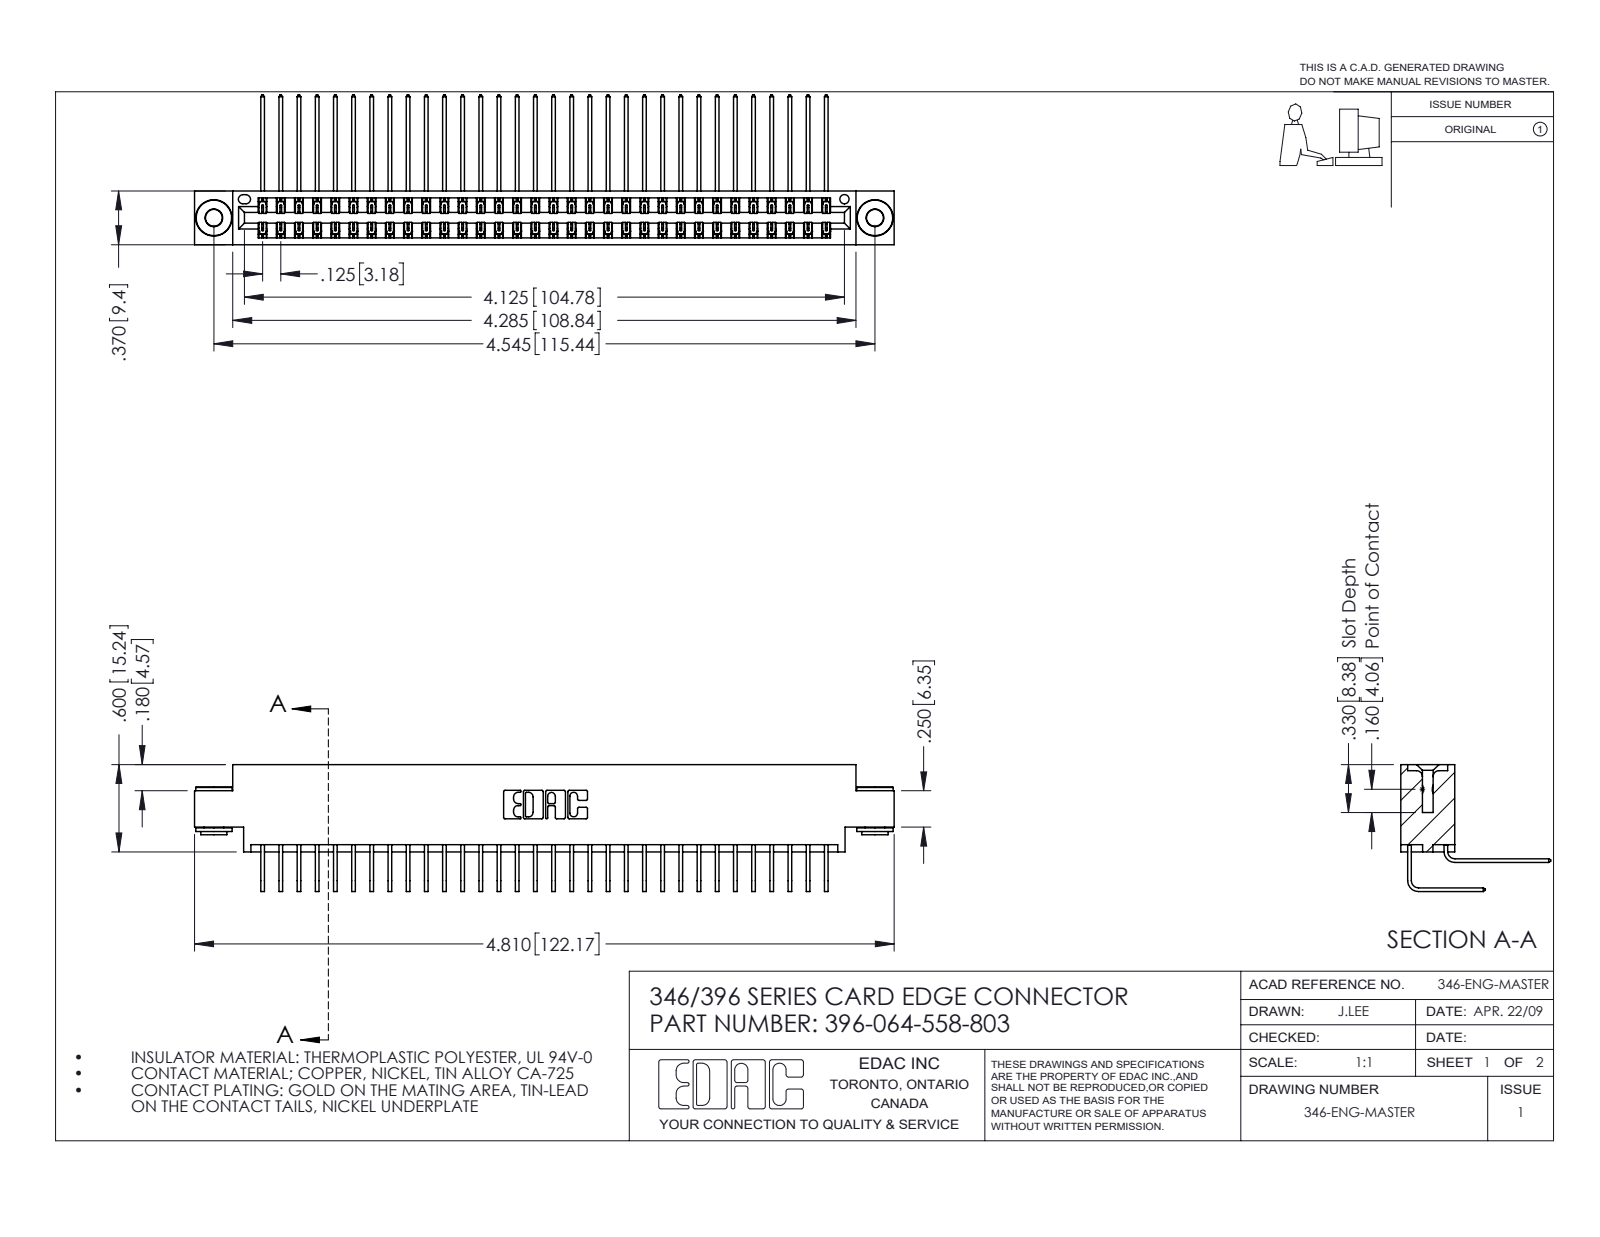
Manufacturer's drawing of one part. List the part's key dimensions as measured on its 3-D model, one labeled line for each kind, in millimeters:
Part name (STEP PRODUCT): 346 Part_0.170 Offset - 0.156 Dia-TH; 345-250-002_345-250-002-102; 345-292-001_558 559 Tail - 1; 345-292-001_558 Tail - 2 (+1 more)
STEP written by: SolidWorks 2016 (CONFIG_CONTROL_DESIGN)
Units: millimetres
Bodies: 67 solids, 3620 faces (2458 planar, 1154 cylindrical, 8 other)
Overall size (bounding box): 122.2 × 26.2 × 22.2
Volume: 12 100 mm³ · Surface area: 18 600 mm²
Round holes (diameter × count): ⌀2.9 ×2, ⌀4 ×2, ⌀1.6 ×1
Round bosses / shafts (diameter × count): ⌀6.4 ×2, ⌀4.6 ×2, ⌀3.5 ×2
Partial cylindrical surfaces — rounded edges, fillets, slot ends (radius × count): R0.2 ×96, R0.3 ×22, R0.2 ×6, R0.8 ×6, R0.7 ×3, R0.4 ×2, R0.6 ×2, R0.6 ×2
Main face-to-face distances: 8.2, 1.2, 0.6, 9.4, 6.4, 7.6, 1.8, 7, 3.8, 5.6
Hole centre spacings: 6.2, 110.2, 115.4
